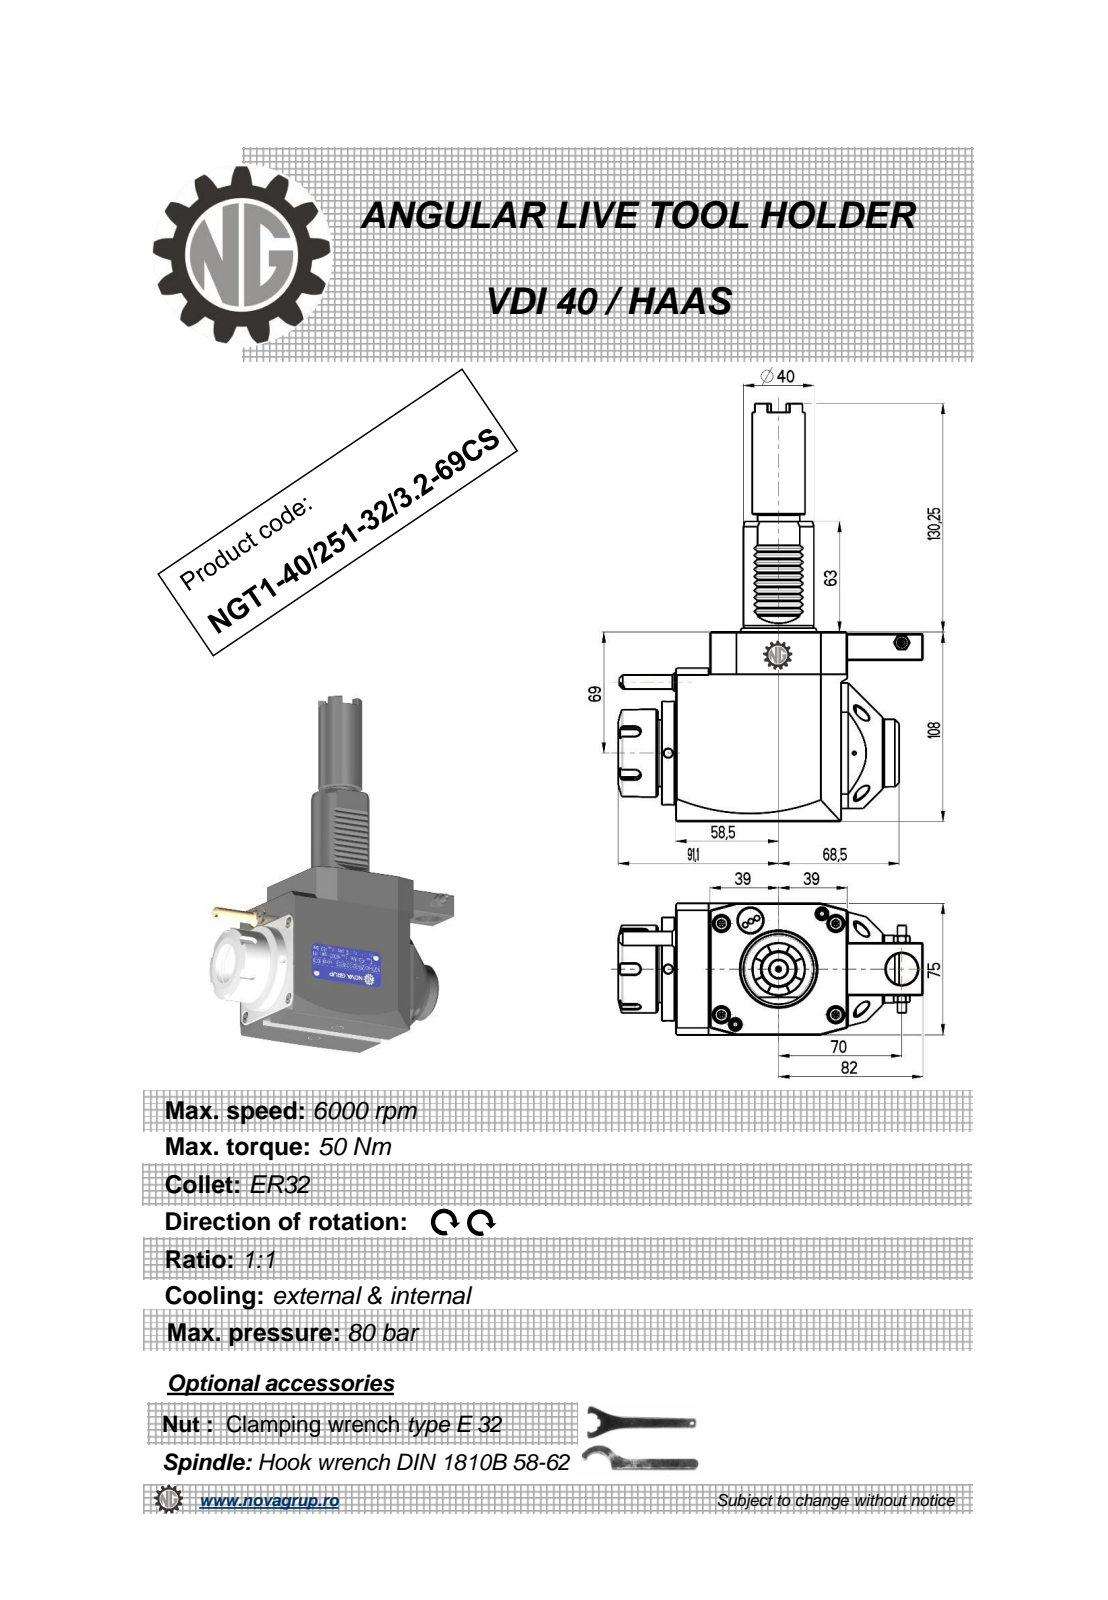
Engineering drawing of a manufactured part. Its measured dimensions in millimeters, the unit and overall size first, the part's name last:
Units: millimetres
Overall size (bounding box): 238.25 × 173.1 × 75
Round holes (diameter × count): ⌀5 ×3, ⌀3 ×1, ⌀4.2 ×1, ⌀9.5 ×1, ⌀18 ×1, ⌀20 ×1, ⌀27 ×1, ⌀46 ×1
Round bosses / shafts (diameter × count): ⌀59 ×1, ⌀50 ×1, ⌀46 ×1, ⌀41 ×1, ⌀40 ×1, ⌀38.5 ×1, ⌀30 ×1, ⌀24 ×1
Partial cylindrical surfaces — rounded edges, fillets, slot ends (radius × count): R0.26 ×12, R0.3 ×10, R0.2 ×6, R3 ×5, R5.8 ×2, R6 ×2, R600 ×2, R0.5 ×1
Main face-to-face distances: 75, 108, 19.5, 27.5, 1, 3.5, 20, 83.5, 8, 22.5
Hole centre spacings: 27.34, 44.12, 61.5, 62.75, 70, 132.75, 146.94
Volume: 1 003 000 mm³ · Surface area: 85 961 mm²
Bodies: 1 solid, 490 faces (243 planar, 97 cylindrical, 150 other)
Part name (STEP PRODUCT): NGT1_40_251_32_3_2_69CS
STEP written by: PRO/ENGINEER BY PARAMETRIC TECHNOLOGY CORPORATION, 2010280 (CONFIG_CONTROL_DESIGN)
